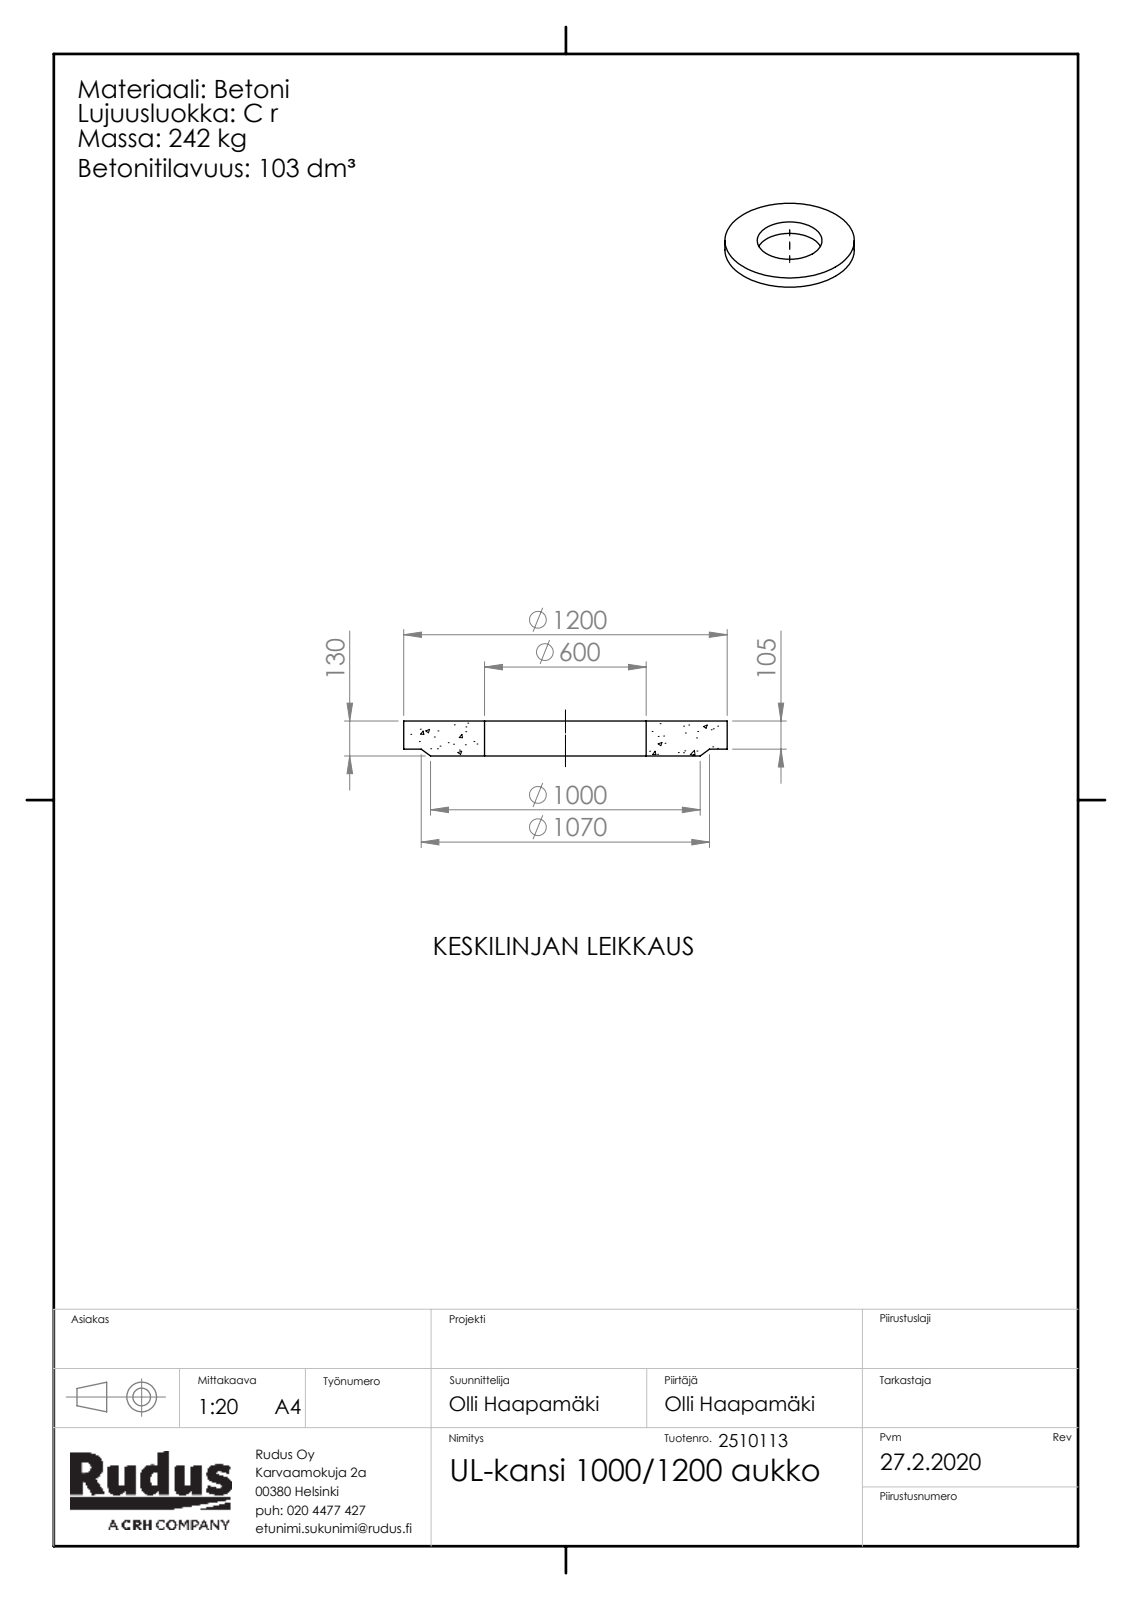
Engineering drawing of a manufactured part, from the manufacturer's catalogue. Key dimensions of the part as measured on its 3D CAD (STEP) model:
Part name (STEP PRODUCT): Rudus 2510113 UL-kansi 1000_1200 aukko; UL-osa-kansi_aukko
STEP written by: SolidWorks 2019 (CONFIG_CONTROL_DESIGN)
Units: millimetres
Bodies: 1 solid, 9 faces (3 planar, 4 cylindrical, 2 other)
Overall size (bounding box): 1200 × 1200 × 130
Volume: 103 000 000 mm³ · Surface area: 2 363 000 mm²
Round holes (diameter × count): ⌀600 ×1
Round bosses / shafts (diameter × count): ⌀1200 ×1
Main face-to-face distances: 130, 25, 105
